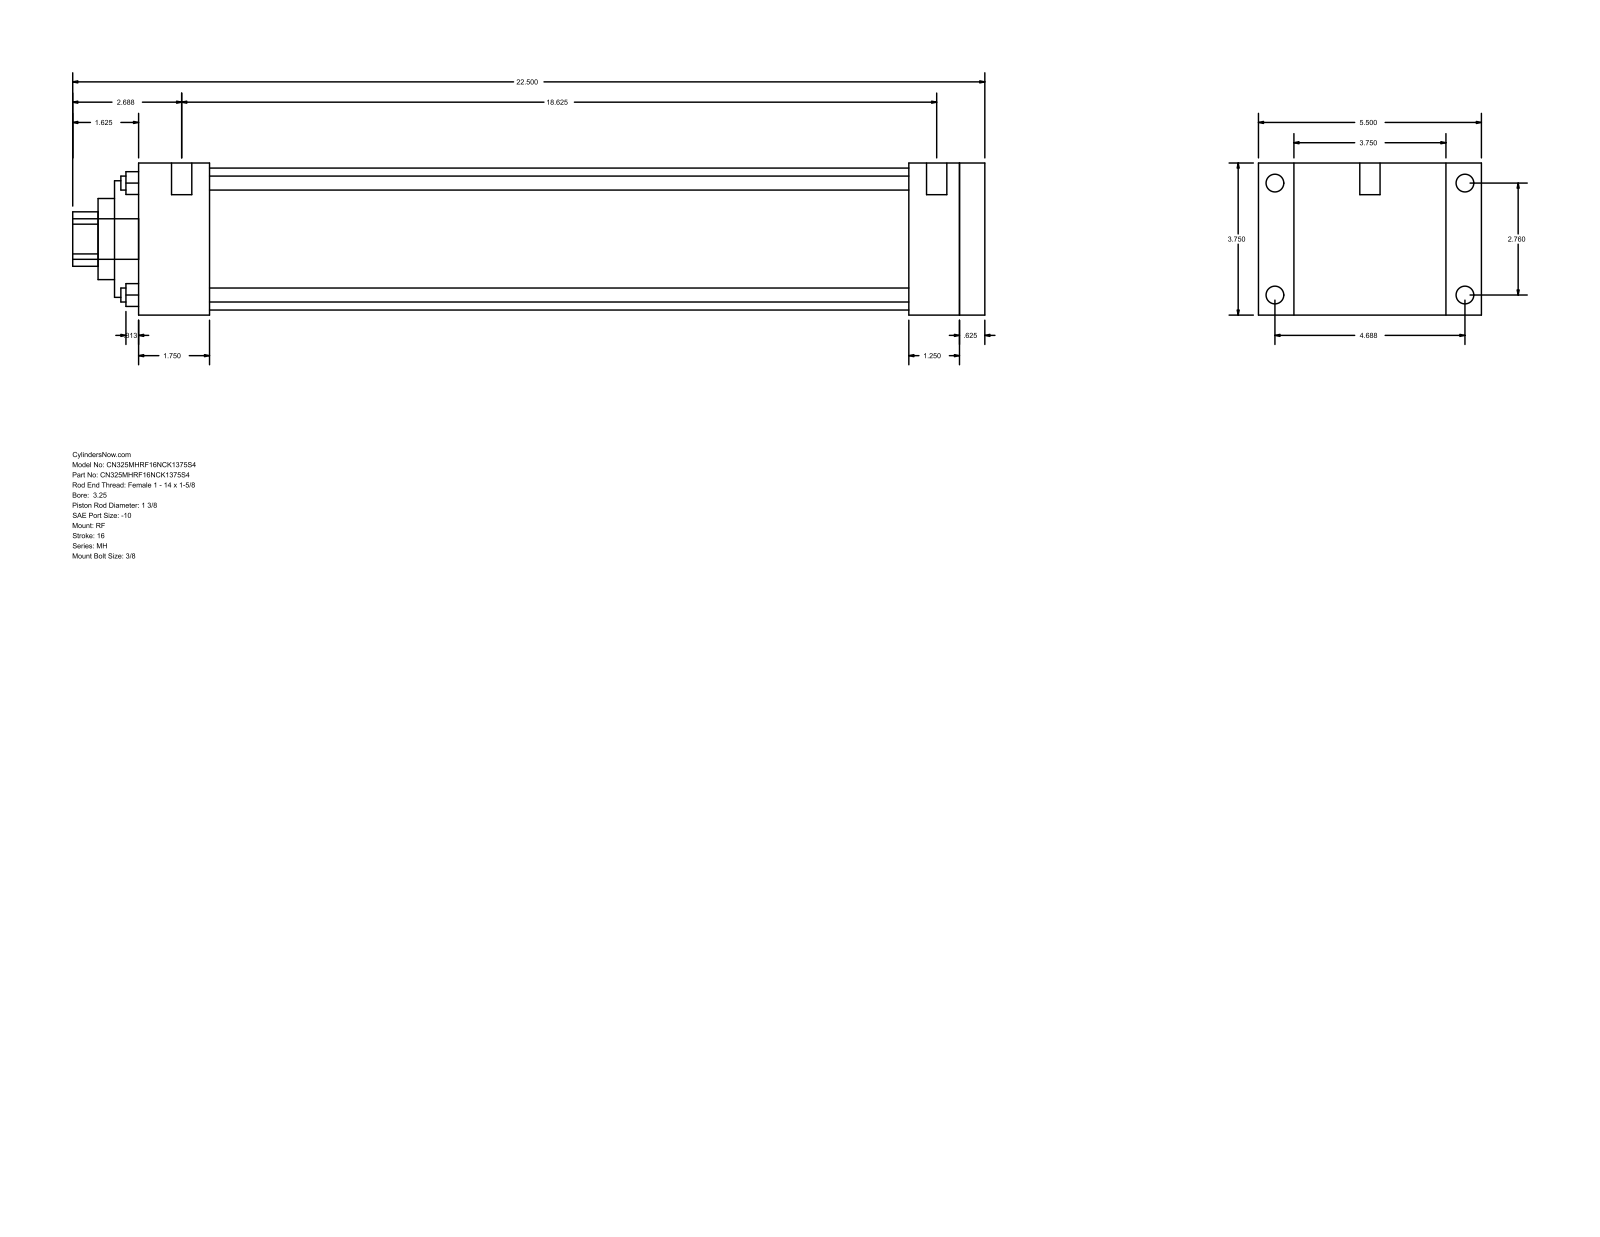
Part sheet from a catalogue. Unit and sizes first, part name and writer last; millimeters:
Units: millimetres
Overall size (bounding box): 571.5 × 139.7 × 95.25
Round holes (diameter × count): ⌀8.76 ×4, ⌀34.92 ×1, ⌀50.8 ×1, ⌀73.03 ×1, ⌀88.9 ×1
Round bosses / shafts (diameter × count): ⌀11.13 ×4, ⌀5.56 ×4, ⌀12.7 ×2, ⌀25.4 ×1
Partial cylindrical surfaces — rounded edges, fillets, slot ends (radius × count): R17.06 ×1
Main face-to-face distances: 95.24, 530.23, 15.88, 514.35, 22.23, 117.47, 44.45, 469.9, 485.78, 482.61
Hole centre spacings: 49.57, 70.1, 99.14
Bodies: 0 solids, 94 faces (65 planar, 29 cylindrical, 0 other)
Part name (STEP PRODUCT): MH_RF__0325_1.375
STEP written by: GSSL Pune (CONFIG_CONTROL_DESIGN)
